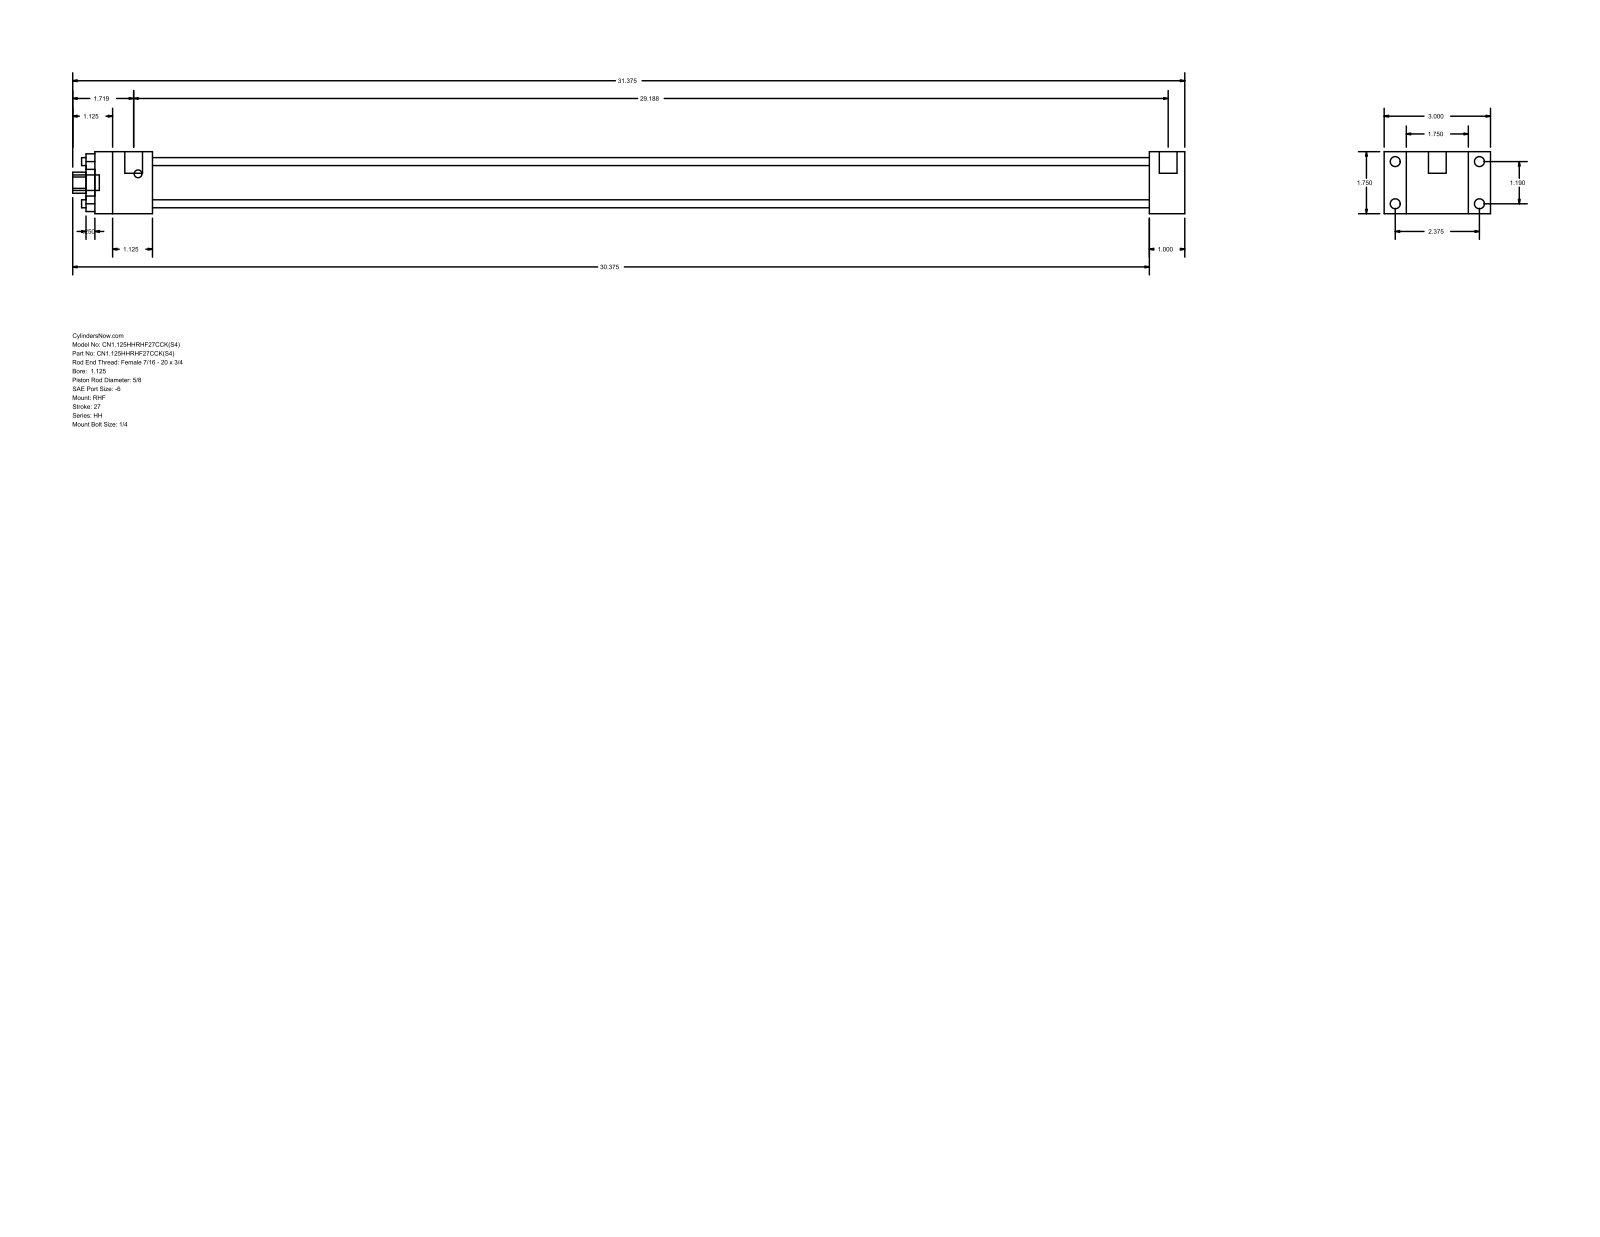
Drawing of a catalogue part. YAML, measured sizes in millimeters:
part_name: "HH_RHF__0112_0.625"
step_written_by: "GSSL Pune (CONFIG_CONTROL_DESIGN)"
units: millimeters
bodies: {solids: 0, faces: 88, planar: 60, cylindrical: 28, other: 0}
overall_size: [796.92, 76.2, 44.45]
round_holes:
  - {diameter: 5.71, count: 4}
  - {diameter: 15.88, count: 1}
  - {diameter: 28.57, count: 1}
  - {diameter: 34.92, count: 1}
round_bosses_or_shafts:
  - {diameter: 7.14, count: 4}
  - {diameter: 5.56, count: 4}
  - {diameter: 12.7, count: 2}
  - {diameter: 11.11, count: 1}
partial_cylinders:
  - {radius: 7.54, count: 1}
face_to_face_distances: [44.46, 15.87, 60.33, 25.4, 76.2, 714.37, 739.77, 41.27, 755.64, 781.04]
hole_center_spacings: [21.37, 30.22, 42.74]
